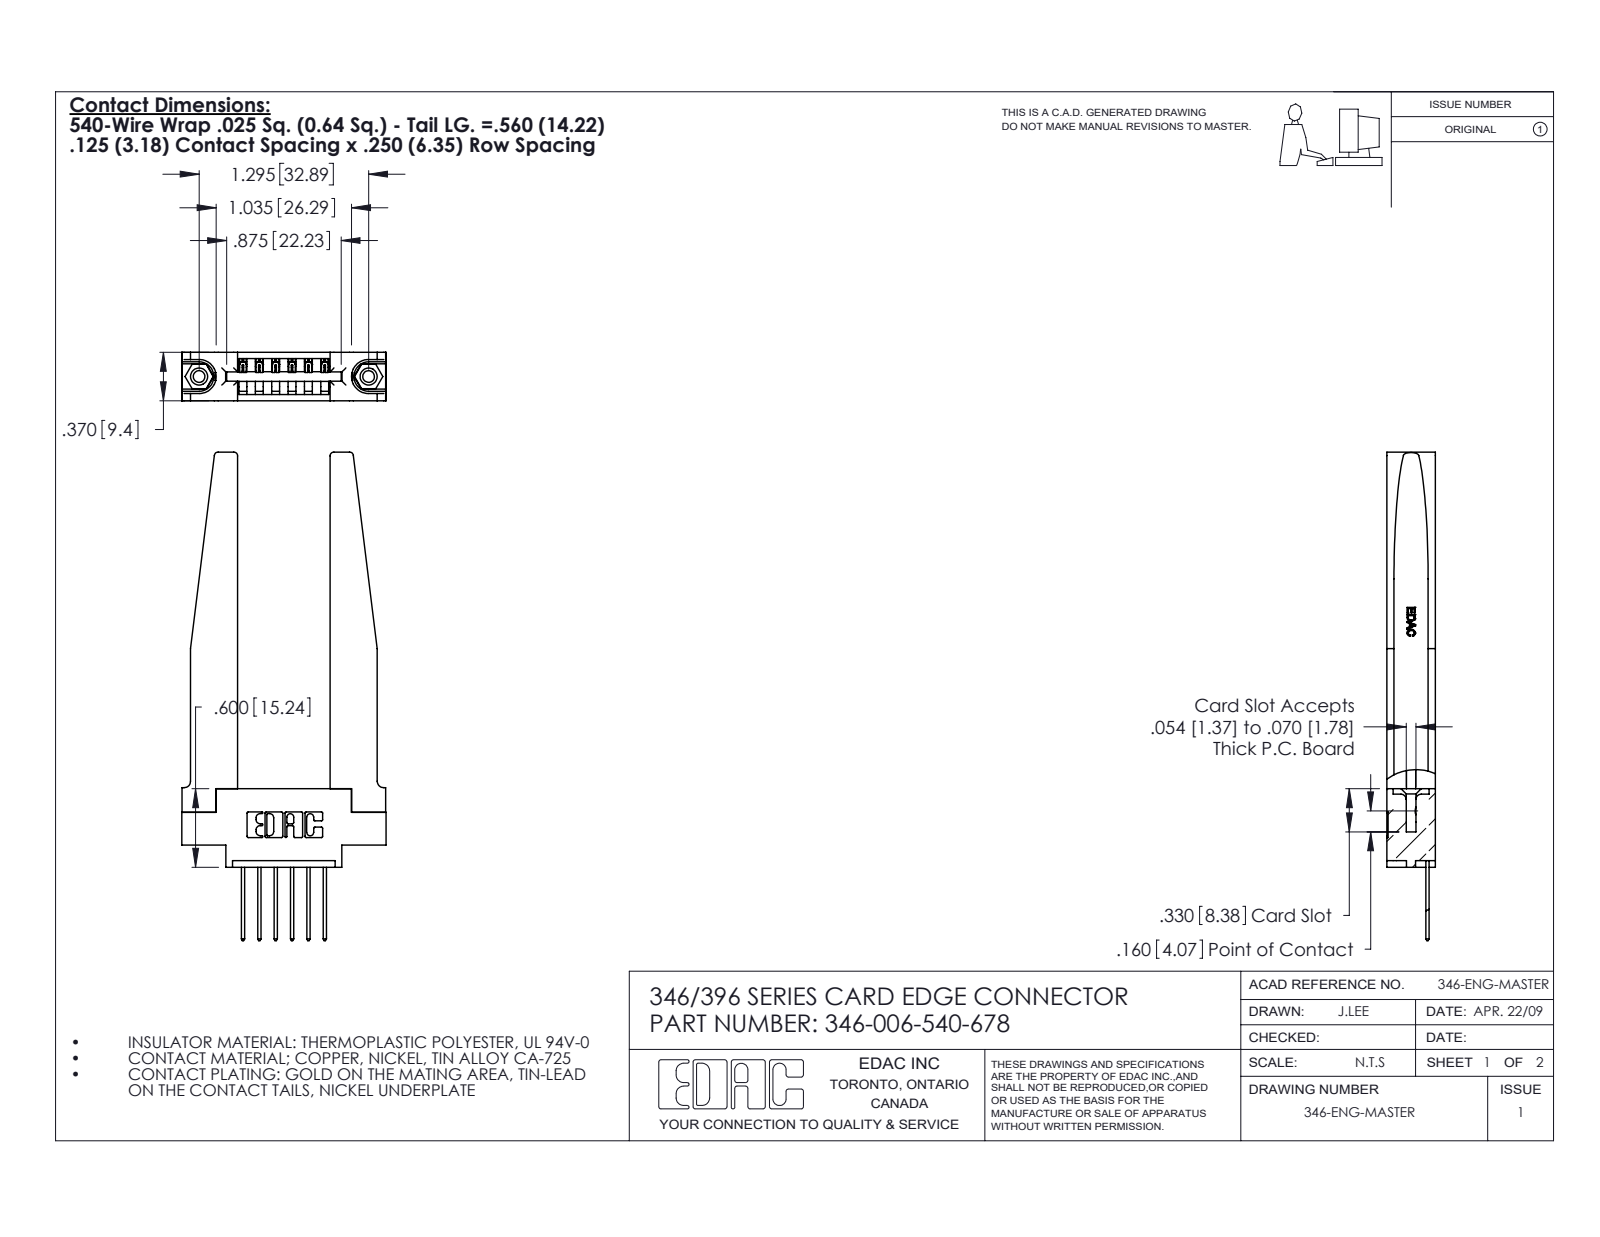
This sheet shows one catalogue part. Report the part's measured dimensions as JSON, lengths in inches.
{"part_name": "346-220-078_345-220-078; 346-006-540-678; 345-292-001_345-293-140; 346 Part_0.170 Offset - 0.156 Dia-TH (+1 more)", "step_written_by": "SolidWorks 2020 (CONFIG_CONTROL_DESIGN)", "units": "inches", "bodies": {"solids": 11, "faces": 722, "planar": 476, "cylindrical": 194, "other": 52}, "overall_size": [3.73, 1.56, 0.37], "volume_in3": 0.628, "surface_area_in2": 16.47, "round_holes": [[0.089, 2], [0.125, 2], [0.156, 2], [0.064, 1]], "round_bosses_or_shafts": [[0.155, 2]], "partial_cylinders_radius": [[0.01, 22], [0.006, 12], [0.01, 12], [0.03, 8], [0.007, 6], [0.031, 6], [0.026, 3], [0.031, 2]], "face_to_face_distances": [0.37, 0.15, 0.22, 0.25, 0.706, 0.072, 0.148, 0.048, 0.322, 0.102], "hole_center_spacings": [0.246, 1.092, 1.295]}
